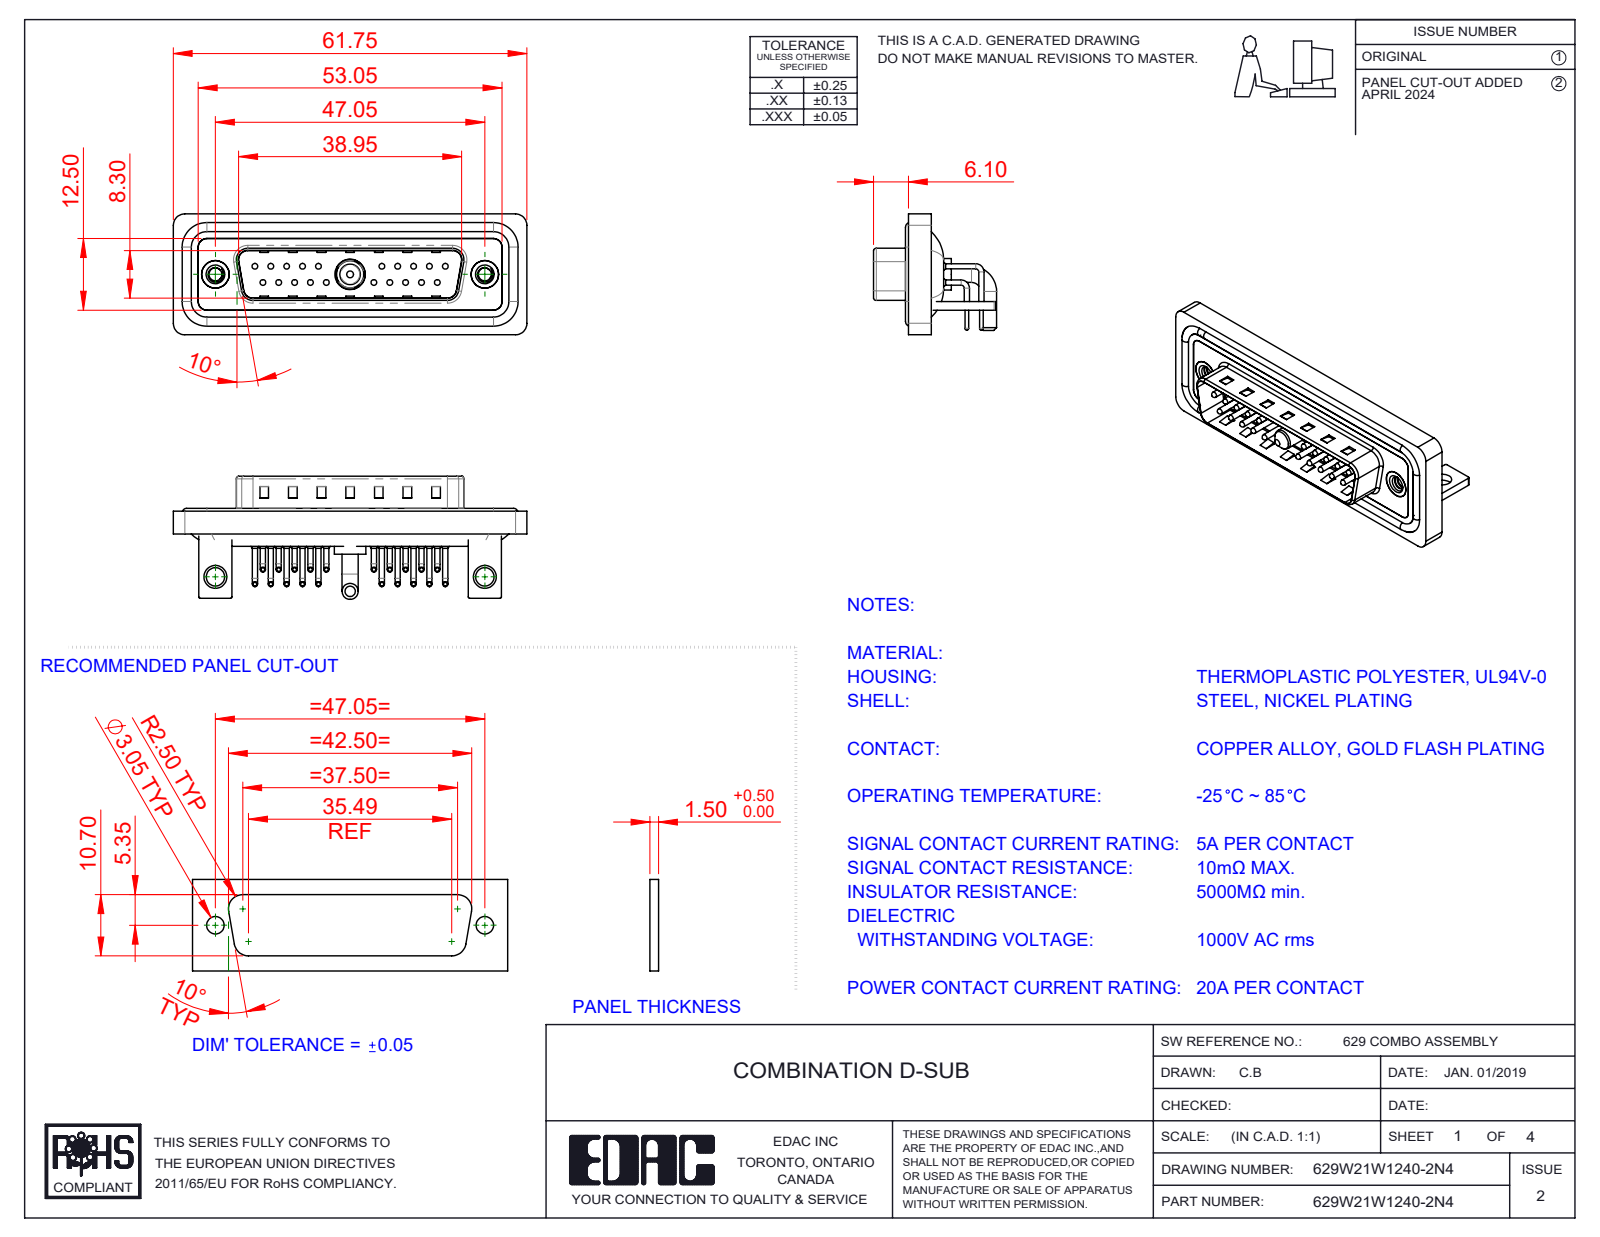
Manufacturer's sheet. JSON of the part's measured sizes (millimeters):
{"part_name": "629Combo Waterproof Housing_25 Contacts; 629Combo Stabilizer Bracket; 629Combo Shell Rear_25 Contacts; 629Combo Contact Row 2 (+6 more)", "step_written_by": "SolidWorks 2023 (CONFIG_CONTROL_DESIGN)", "units": "millimeters", "bodies": {"solids": 31, "faces": 2766, "planar": 1519, "cylindrical": 947, "other": 300}, "overall_size": [61.75, 21.5, 21.1], "volume_mm3": 7695, "surface_area_mm2": 13308, "round_holes": [[0.75, 20], [1.6, 20], [2, 20], [2.26, 2], [3.2, 2], [4, 2], [4.8, 2], [5, 2], [4.85, 1], [5.3, 1]], "round_bosses_or_shafts": [[0.9, 40], [1.5, 20], [1, 20], [0.65, 20], [1.6, 4], [4.9, 2], [2.8, 2], [5.5, 1]], "partial_cylinders_radius": [[1.01, 20], [2, 19], [1.5, 18], [0.25, 16], [0.5, 9], [1.6, 8], [0.6, 4], [0.65, 4]], "face_to_face_distances": [0.4, 0.8, 2.1, 2.9, 1.5, 1.1, 4.1, 1.6, 4.5, 3.7], "hole_center_spacings": [3.16, 2.77, 5.54, 8.31, 5.04, 19.39, 20.97, 22.16]}
